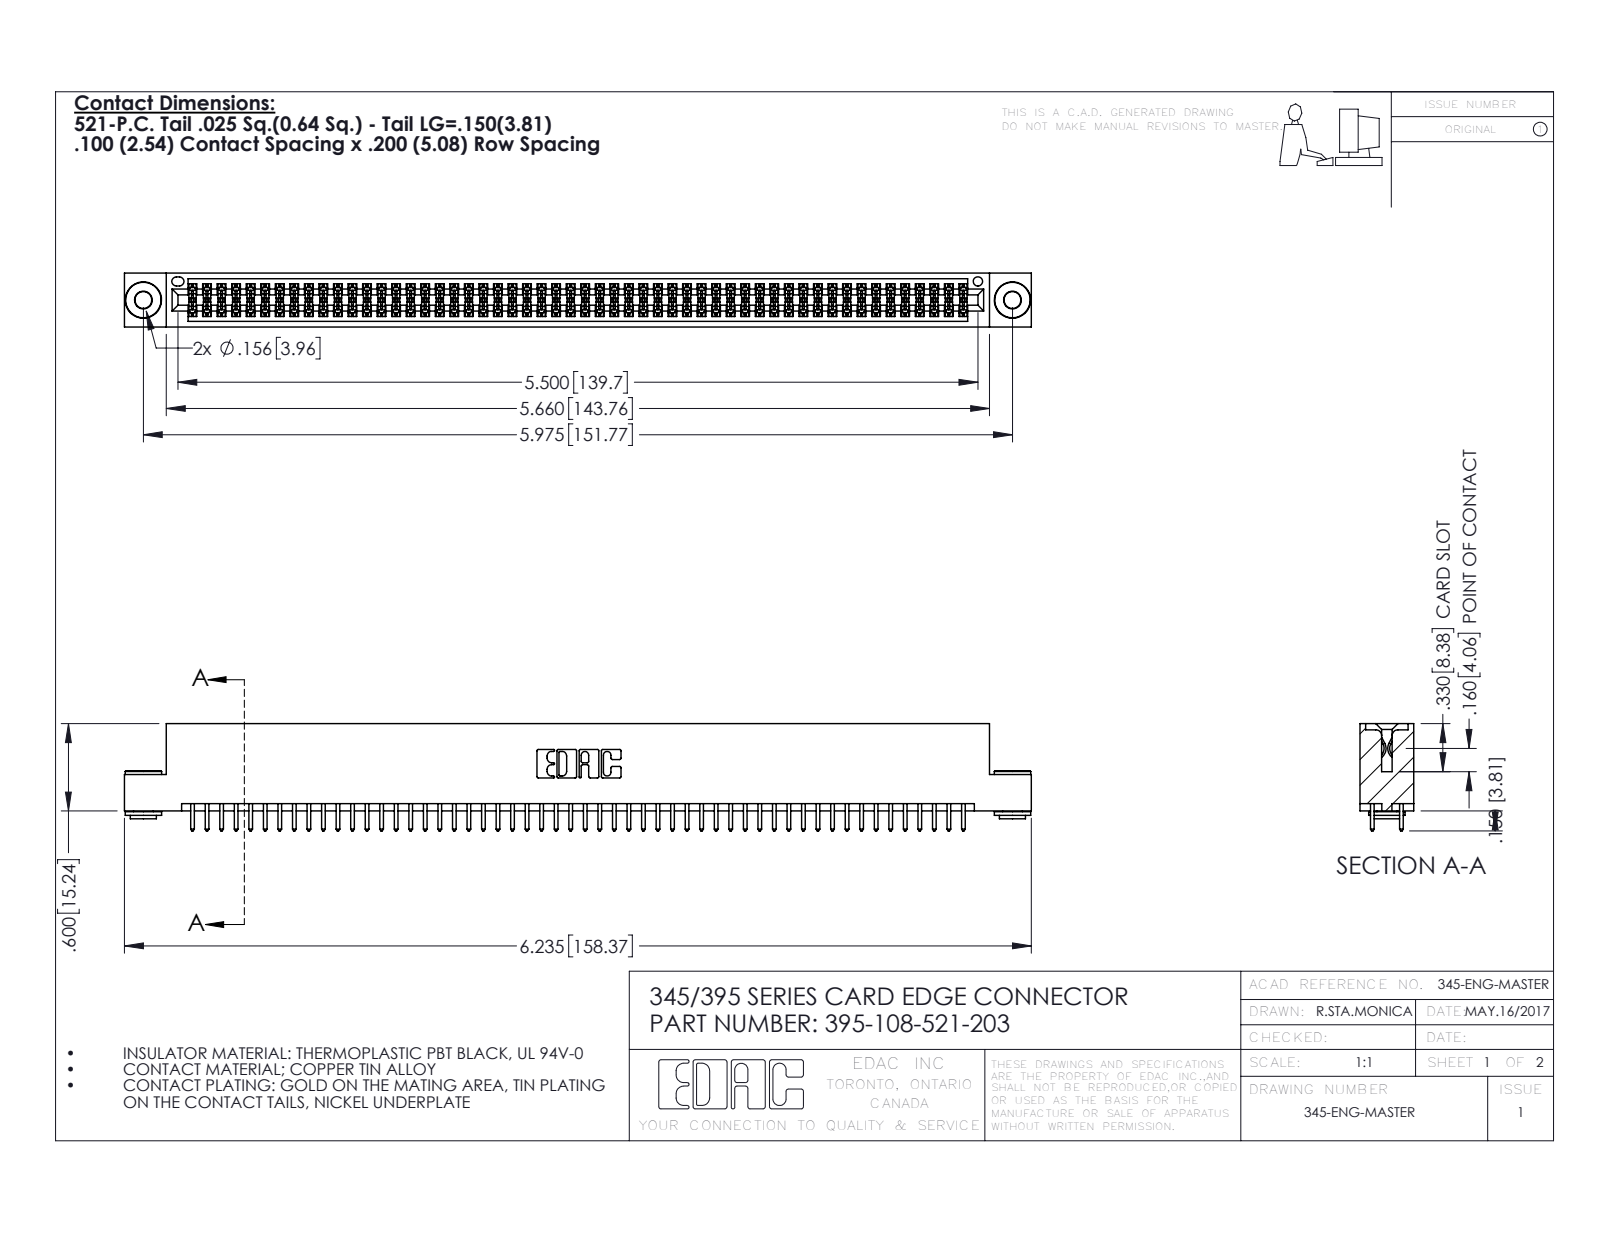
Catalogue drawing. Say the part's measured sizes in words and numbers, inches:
The part is named "395-108-521-203; 345 Part_Flush Mounting Lugs - 0.156 Dia-TH; 345-250-002_345-250-002-102; 345-292-001_345-293-121". Its 3-D file was written by "SolidWorks 2016 (CONFIG_CONTROL_DESIGN)". It is 111 solids with 5564 faces: 3654 planar, 1902 cylindrical and 8 other. Overall it measures 6.235 by 0.737 by 0.37 inches. Its volume is 0.944 cubic inches and its surface area 35.68 square inches. Round holes: 2 of diameter 0.116, 2 of diameter 0.156, 1 of diameter 0.064. Round bosses or shafts: 2 of diameter 0.25, 2 of diameter 0.18, 2 of diameter 0.136. Partial cylindrical surfaces (rounded edges, fillets, slot ends): 162 of radius 0.006, 108 of radius 0.01, 22 of radius 0.01, 6 of radius 0.007, 6 of radius 0.031, 3 of radius 0.026, 2 of radius 0.014, 2 of radius 0.019. The main face-to-face distances are 0.072, 0.298, 0.2, 0.025, 0.37, 0.098, 0.272, 0.225, 0.175, 0.149. The hole center spacings are 0.27, 5.739, 5.975.
